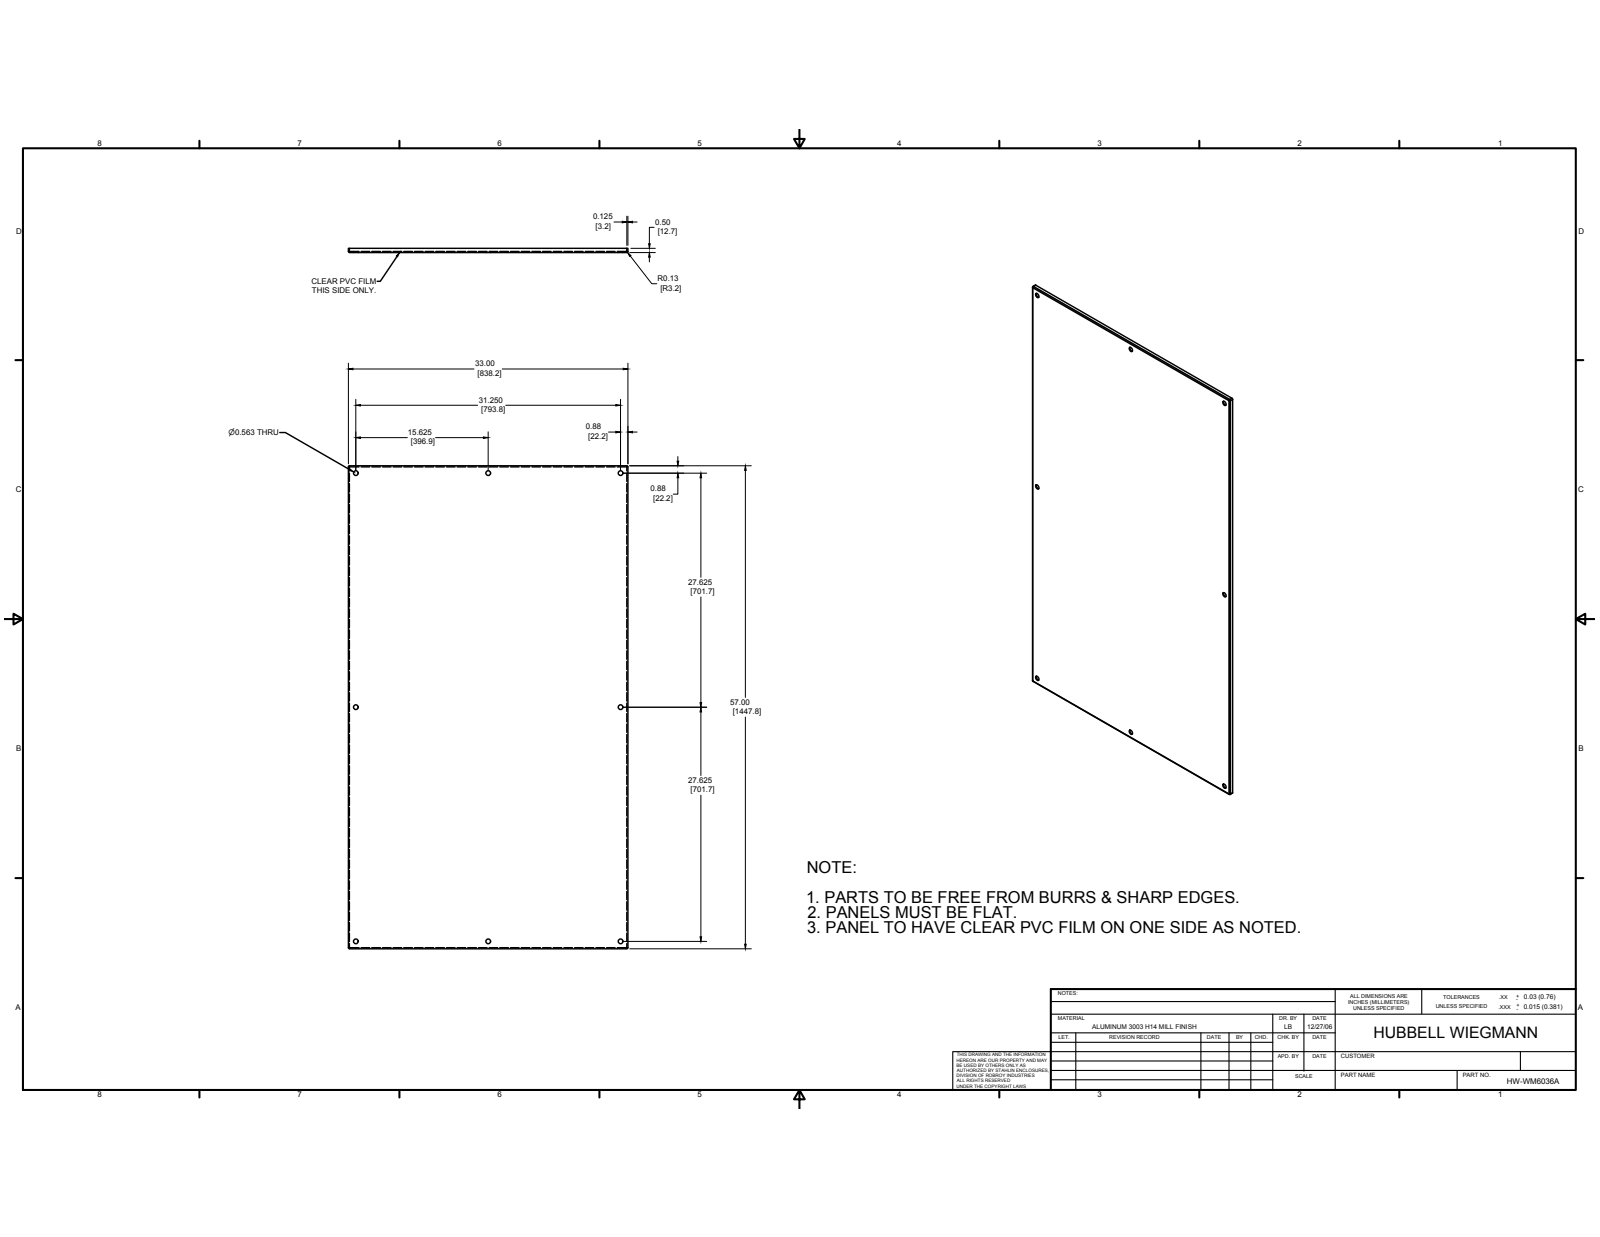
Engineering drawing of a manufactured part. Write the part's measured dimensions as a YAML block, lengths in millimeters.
part_name: "BP6036AL_STP"
step_written_by: "Autodesk Inventor 2014 (AUTOMOTIVE_DESIGN)"
units: millimeters
bodies: {solids: 1, faces: 31, planar: 11, cylindrical: 16, other: 4}
overall_size: [1447.8, 838.2, 12.7]
volume: 3977000
surface_area: 2521000
round_holes:
  - {diameter: 14.29, count: 8}
partial_cylinders:
  - {radius: 3.17, count: 8}
face_to_face_distances: [3.18, 835.02, 1444.62, 9.52, 12.7, 838.2, 831.84, 1447.8, 1441.44]
hole_center_spacings: [396.88, 701.67, 806.14, 1059.43, 1458.38, 793.76, 1403.34, 1612.27]
